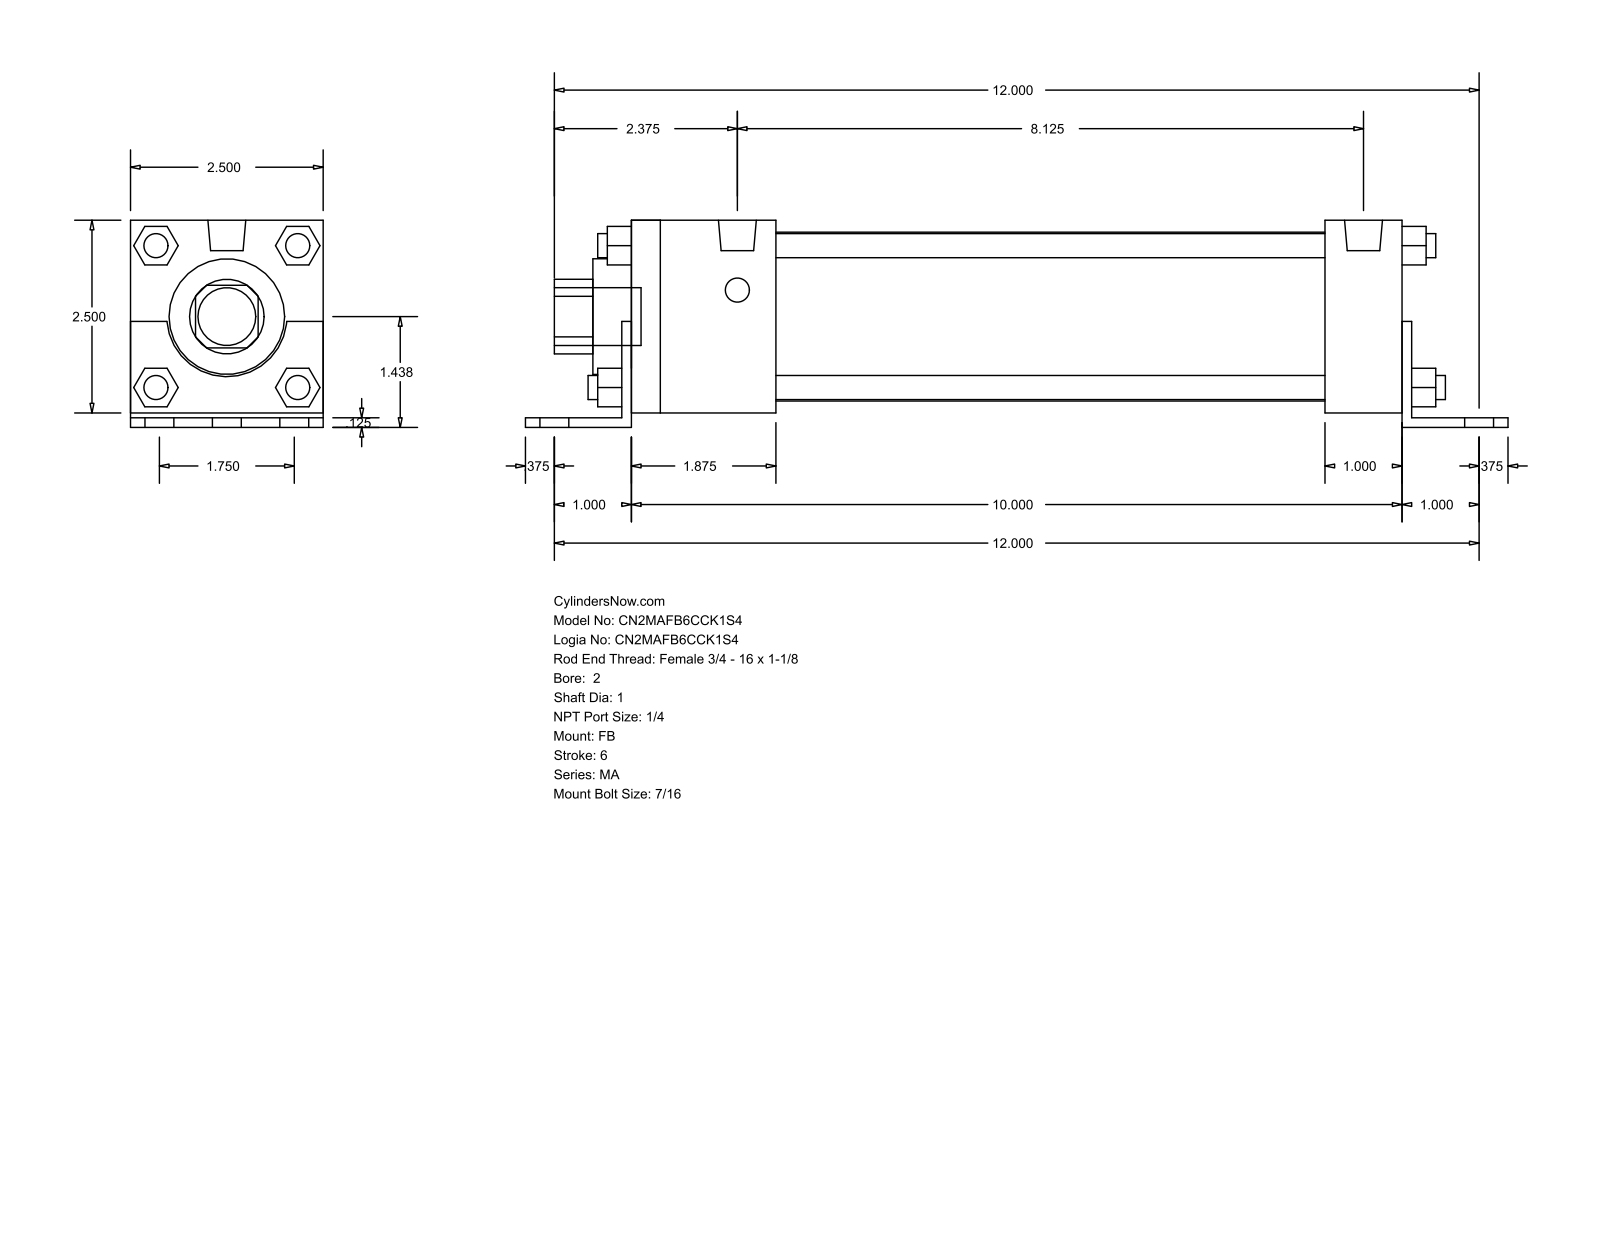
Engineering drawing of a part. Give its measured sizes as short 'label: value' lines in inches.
name: MA_FB__0200_1
written by: GSSL Pune (CONFIG_CONTROL_DESIGN)
unit: in
bodies: 0 solids, 140 faces (105 planar, 35 cylindrical, 0 other)
size: 12.75 × 2.687 × 2.5
holes: 1× ⌀1, 1× ⌀1.5, 1× ⌀2.19
bosses: 8× ⌀0.313, 6× ⌀0.437, 2× ⌀0.492, 1× ⌀0.75
rounds: 1× R0.484, 1× R0.78
face distances: 2.5, 0.125, 0.187, 2.687, 0.063, 2.563, 10.125, 0.5, 10, 1
